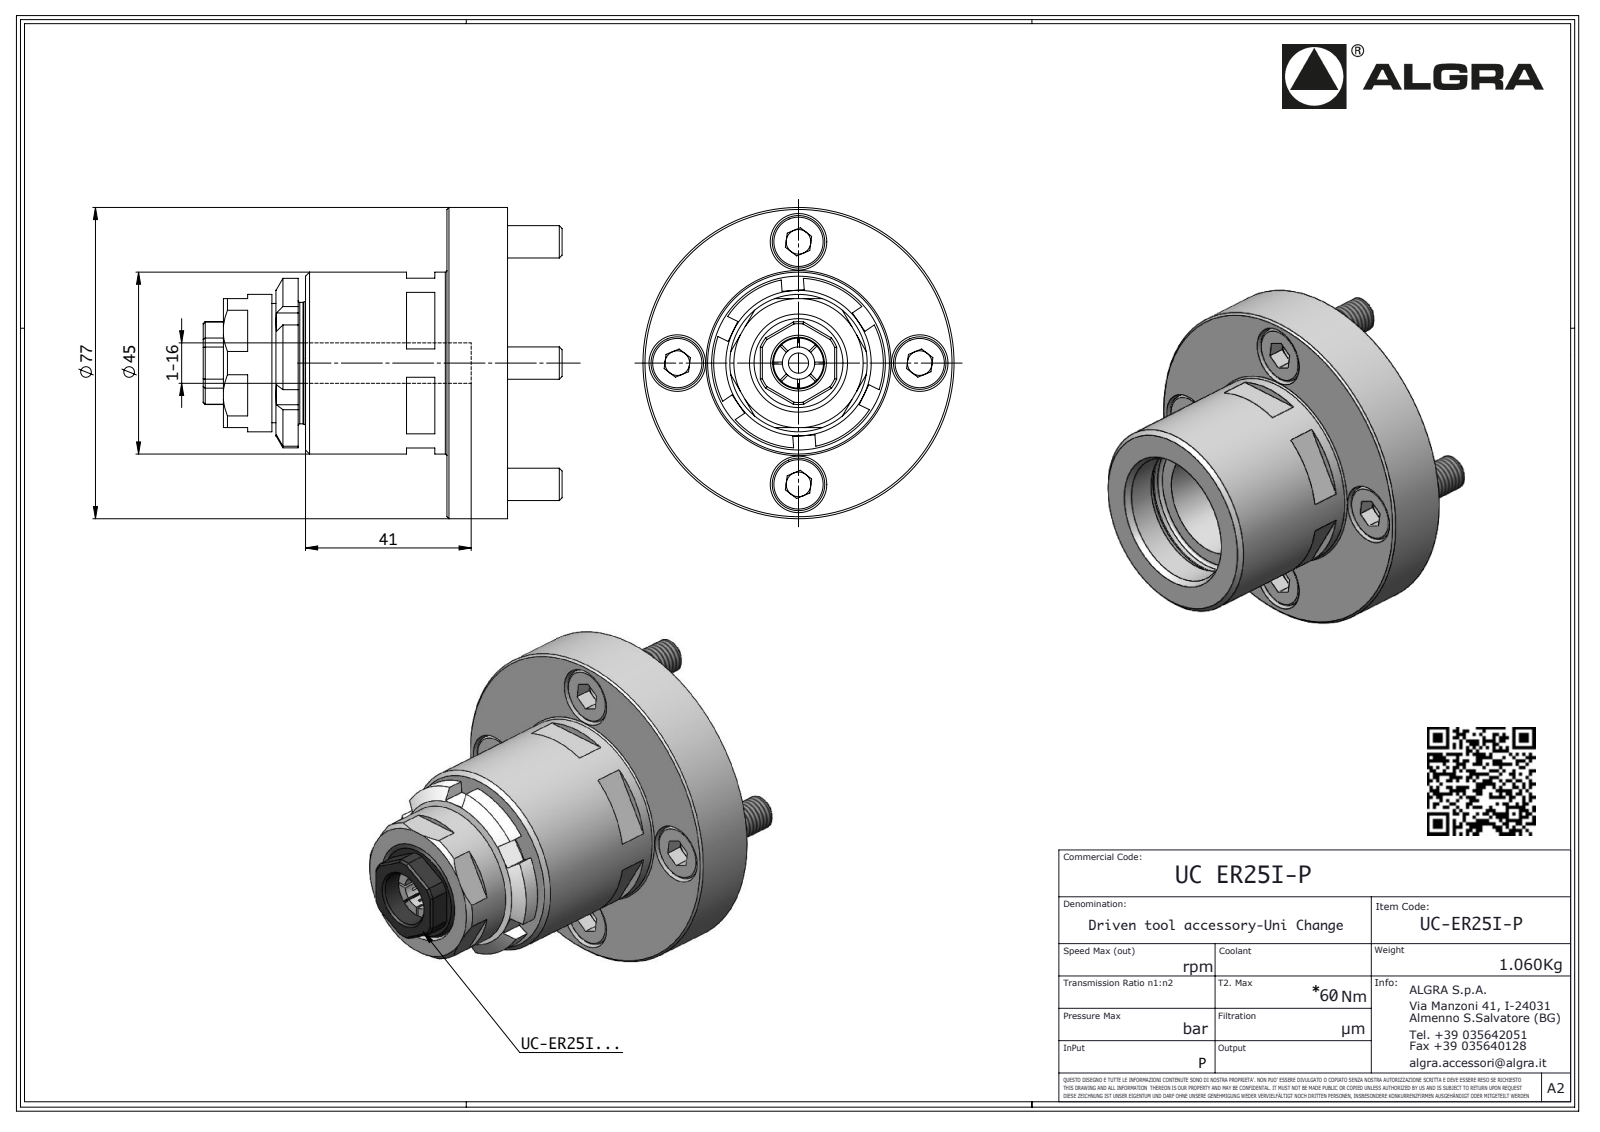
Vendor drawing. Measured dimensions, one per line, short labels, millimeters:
name: UCER25I-P
written by: SolidWorks 2016 (AUTOMOTIVE_DESIGN)
unit: mm
bodies: 1 solid, 356 faces (232 planar, 49 cylindrical, 75 other)
size: 88.82 × 77 × 77
volume: 148 026 mm³; area: 24 204 mm²
holes: 1× ⌀2.1, 1× ⌀30.5
bosses: 4× ⌀8, 1× ⌀77, 1× ⌀45, 1× ⌀34, 1× ⌀30.05, 1× ⌀29.5, 1× ⌀24.95, 1× ⌀6.37
rounds: 7× R0.33, 7× R0.52, 7× R3.7, 1× R0.21, 1× R10.25, 1× R21
face distances: 15, 50, 35, 36.82, 51.82, 1.82, 70.32, 55.32, 20.32, 18.5
hole spacings: 29.37
